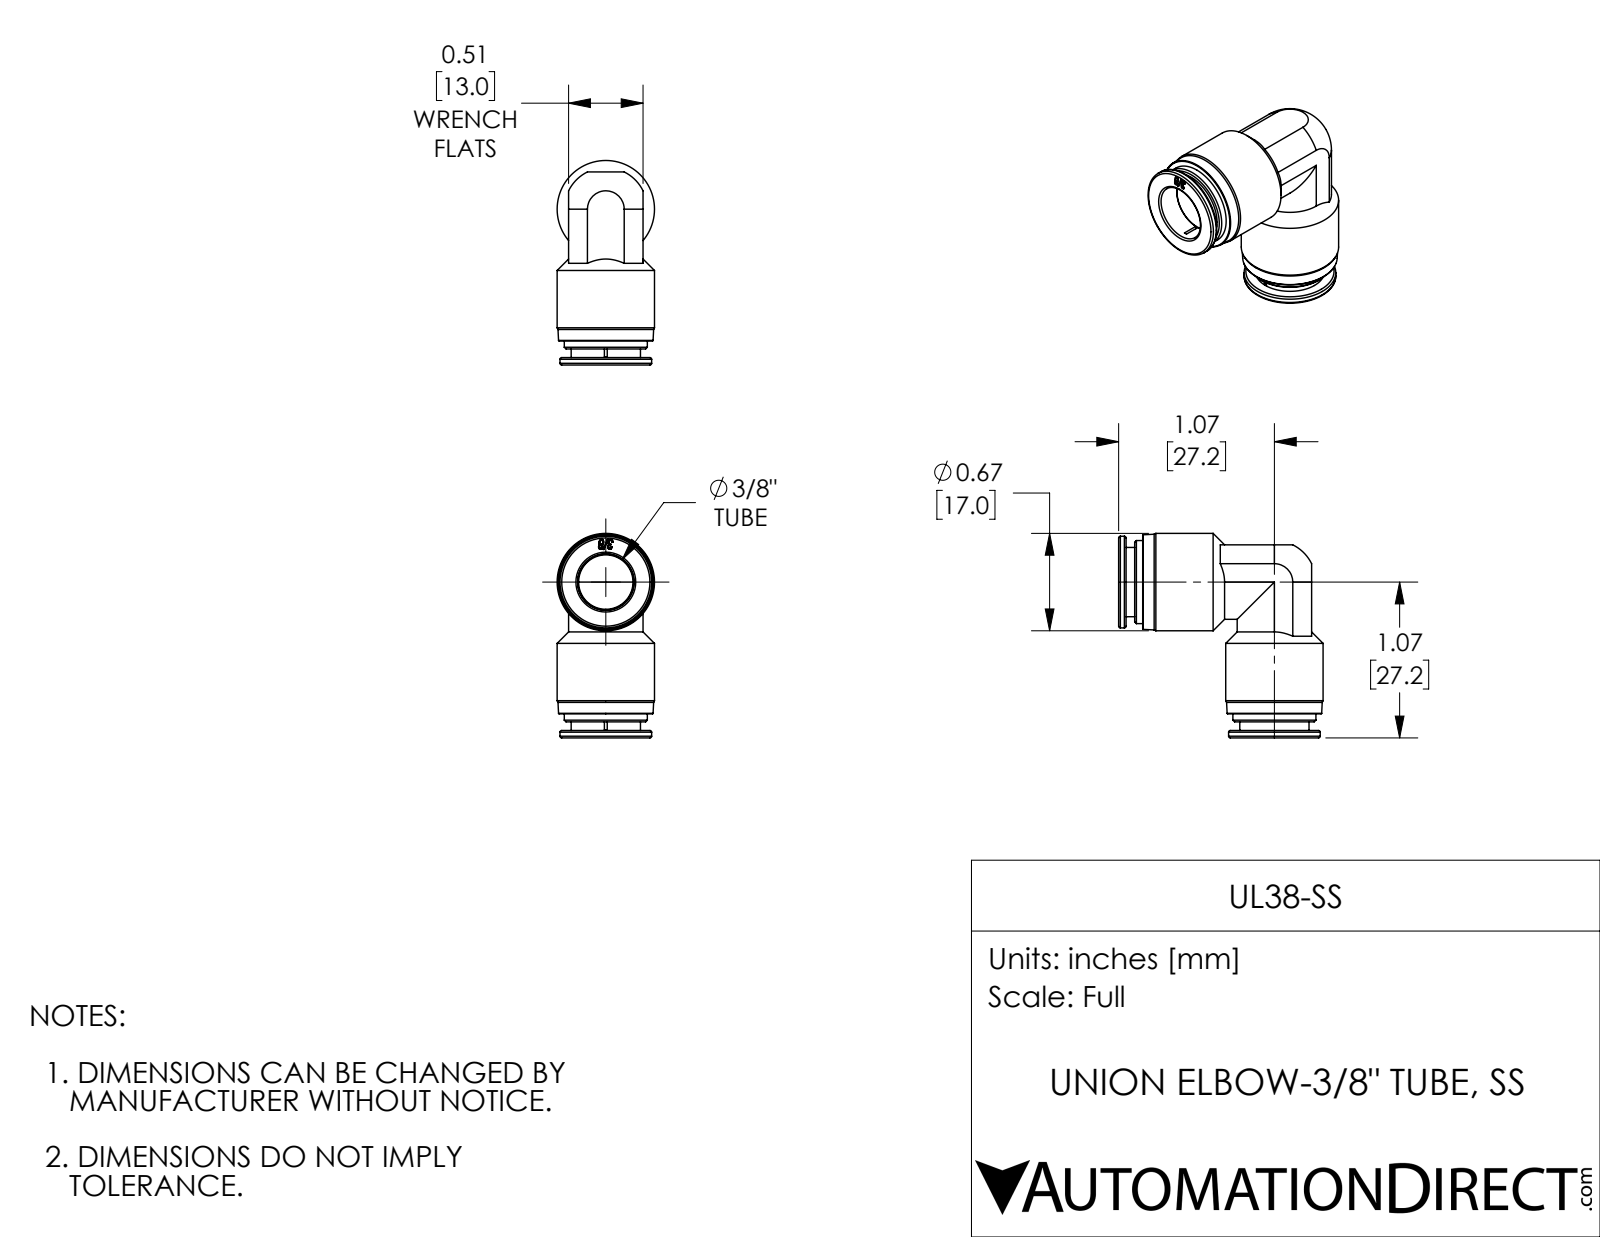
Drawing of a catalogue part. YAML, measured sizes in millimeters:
part_name: "UL38-SS"
step_written_by: "SolidWorks 2017 (AUTOMOTIVE_DESIGN)"
units: millimeters
bodies: {solids: 1, faces: 193, planar: 52, cylindrical: 35, other: 106}
overall_size: [35.7, 35.7, 17]
volume: 6050
surface_area: 5123
round_holes:
  - {diameter: 9.5, count: 2}
  - {diameter: 9.8, count: 2}
  - {diameter: 9.9, count: 2}
round_bosses_or_shafts:
  - {diameter: 17, count: 2}
  - {diameter: 16, count: 2}
  - {diameter: 14.5, count: 2}
  - {diameter: 12.1, count: 2}
partial_cylinders:
  - {radius: 6.5, count: 2}
face_to_face_distances: [33.7, 1.3, 32.4, 4.2, 2.9, 29.5, 13, 1.4, 2.8, 1.5]
